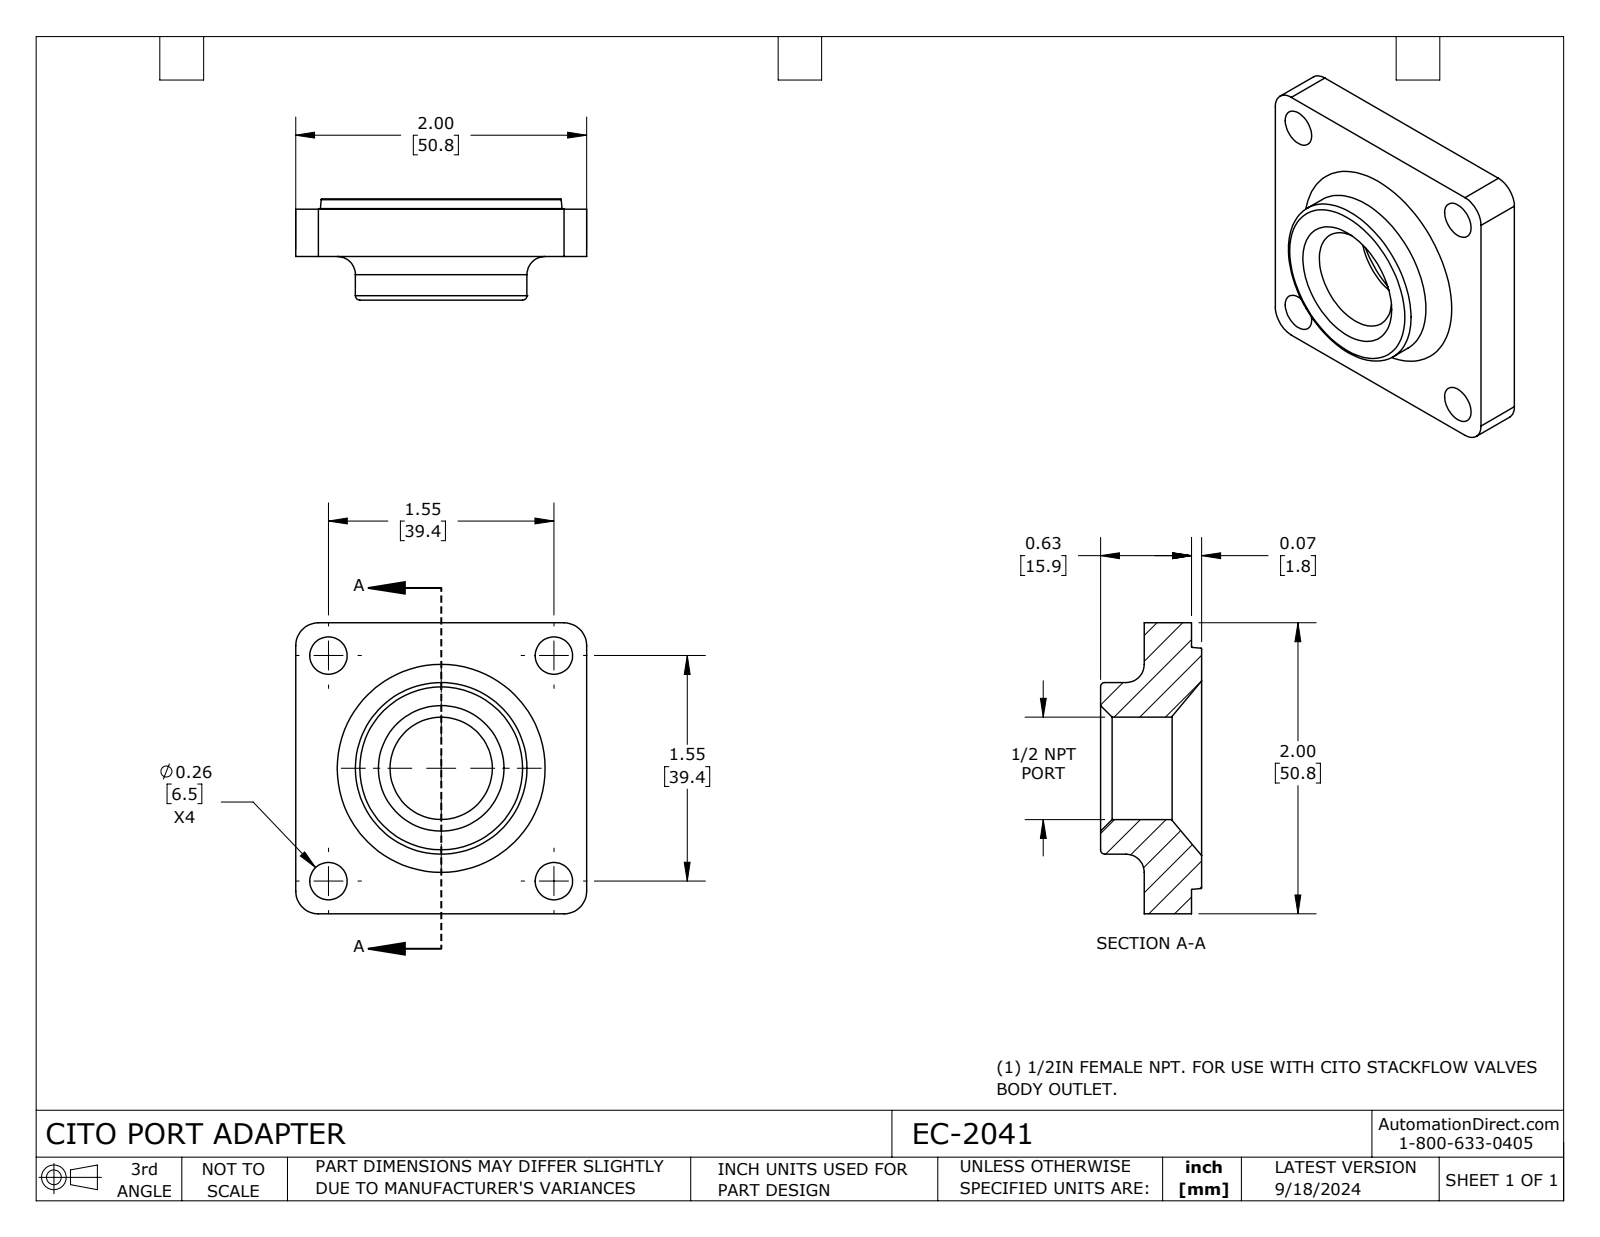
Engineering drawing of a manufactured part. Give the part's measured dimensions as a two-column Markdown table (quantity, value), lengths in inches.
| quantity | value |
| --- | --- |
| part name | EC-2041 |
| STEP written by | SolidWorks 2023 (CONFIG_CONTROL_DESIGN) |
| units | inches |
| bodies | 1 solid, 40 faces (9 planar, 17 cylindrical, 14 other) |
| overall size | 2 × 2 × 0.695 |
| volume | 1.368 in³ |
| surface area | 12.73 in² |
| round holes (diameter × count) | 0.257 × 4, 0.703 × 1 |
| round bosses / shafts (diameter × count) | 1.179 × 1 |
| partial cylindrical surfaces (radius × count) | 0.156 × 4 |
| main face-to-face distances | 0.325, 2, 0.395, 0.07, 0.3, 0.625, 0.695, 0.492, 0.192, 0.133 |
| hole center spacings | 1.096, 1.55, 1.096, 1.55, 2.192, 2.193 |
